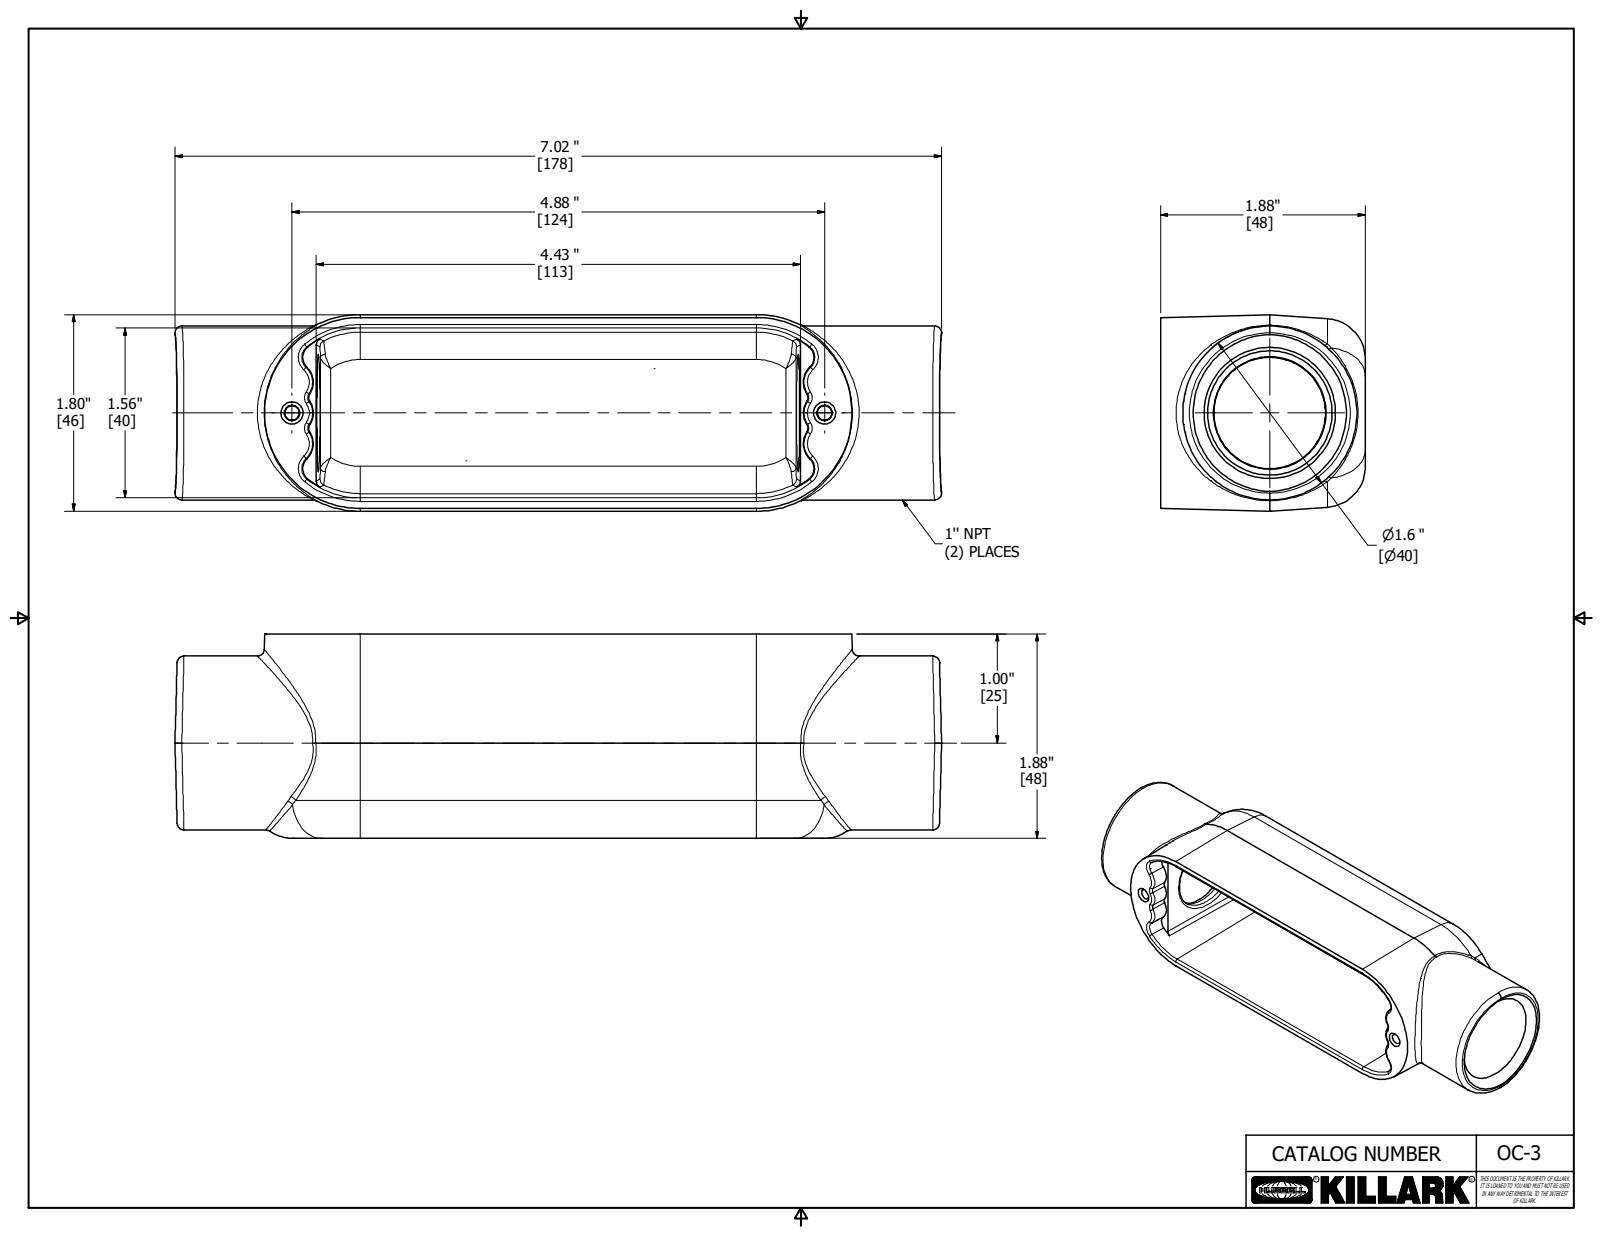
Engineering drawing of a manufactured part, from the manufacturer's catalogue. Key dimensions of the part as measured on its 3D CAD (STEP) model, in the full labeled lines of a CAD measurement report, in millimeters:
Part name (STEP PRODUCT): 18172-1
STEP written by: Autodesk Inventor 2018 (AUTOMOTIVE_DESIGN)
Units: millimetres
Bodies: 1 solid, 149 faces (29 planar, 14 cylindrical, 106 other)
Overall size (bounding box): 178.2 × 47.6 × 45.8
Volume: 88 240 mm³ · Surface area: 47 250 mm²
Round bosses / shafts (diameter × count): ⌀40.5 ×1
Partial cylindrical surfaces — rounded edges, fillets, slot ends (radius × count): R0.8 ×4, R0.8 ×2, R2.4 ×2, R6.4 ×2, R9.5 ×2
Main face-to-face distances: 42, 2.4, 0.8, 3.2, 47.6, 45.2, 44.4, 1.6, 46.8, 41.3
